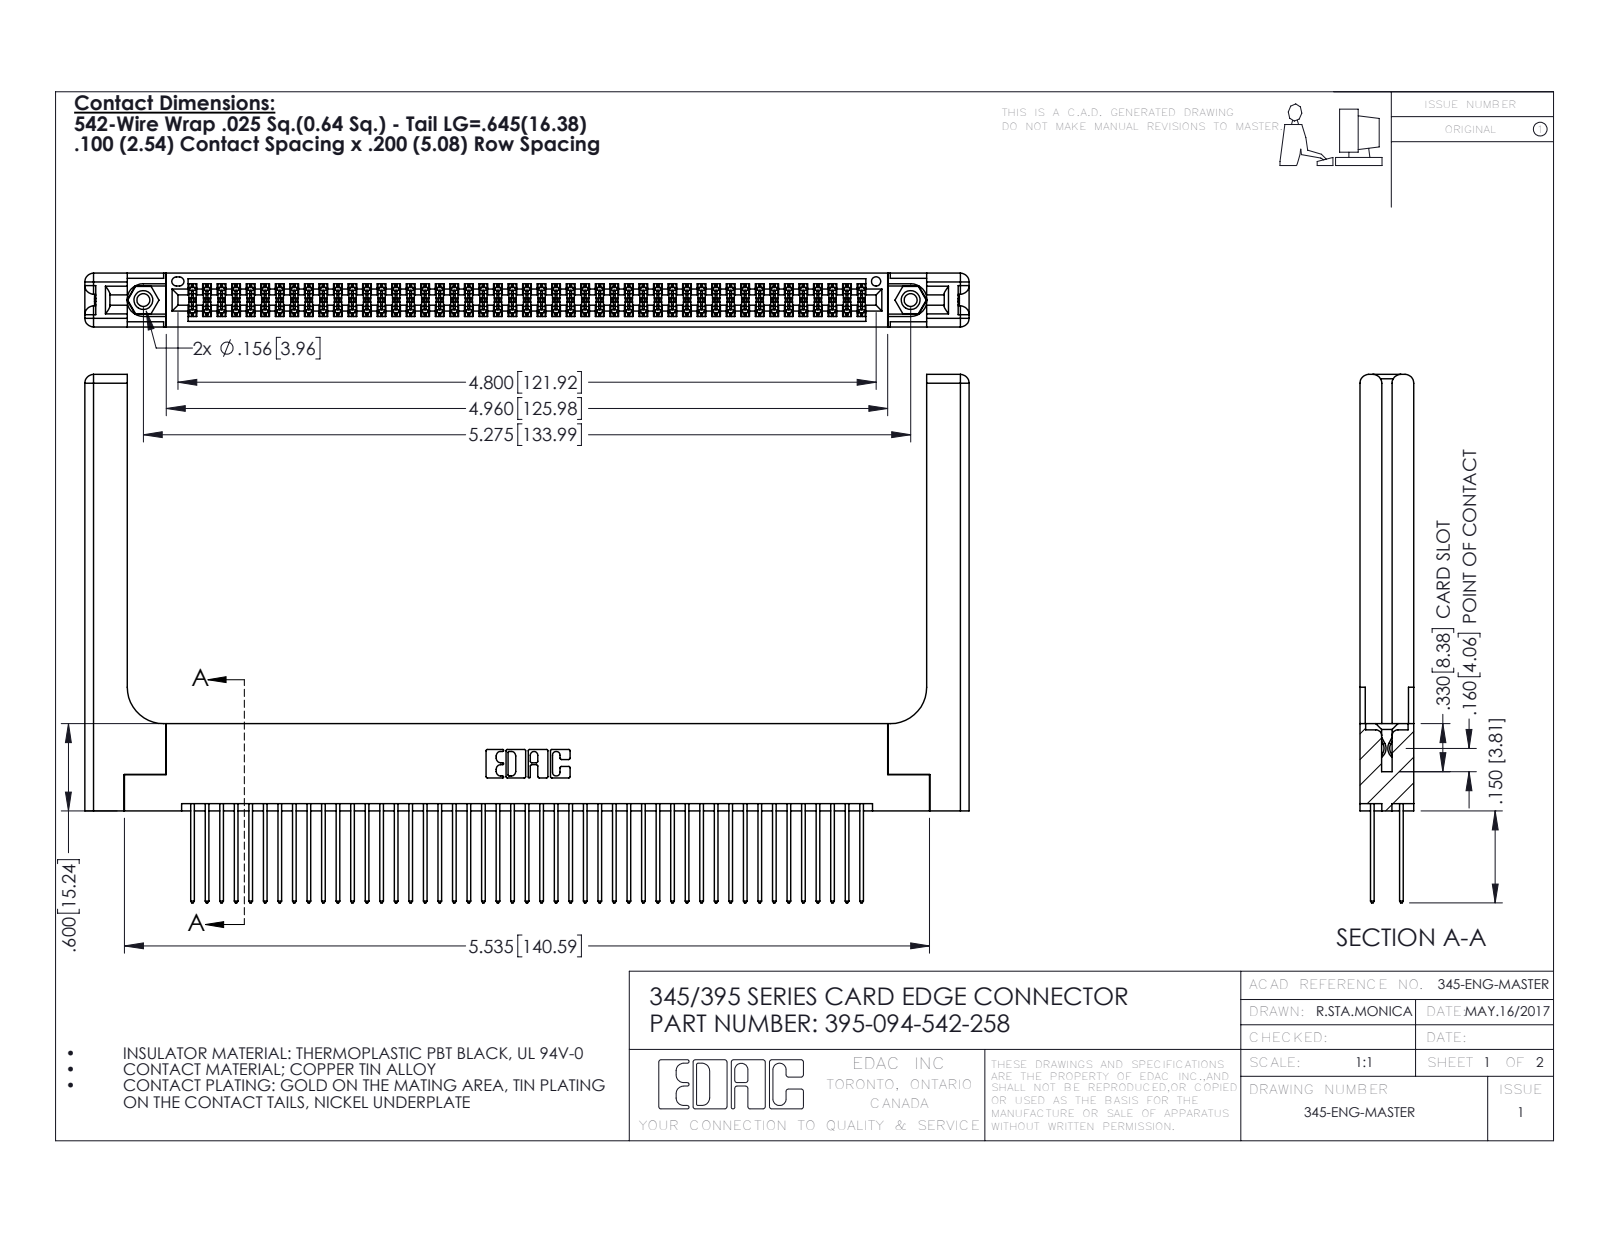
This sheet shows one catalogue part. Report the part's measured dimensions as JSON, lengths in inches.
{"part_name": "345-250-001_345-250-001-102; 395-094-542-258; 345-292-001_345-293-142; 345 Part_Flush Mounting Lugs - 0.156 Dia-TH (+1 more)", "step_written_by": "SolidWorks 2016 (CONFIG_CONTROL_DESIGN)", "units": "inches", "bodies": {"solids": 99, "faces": 5082, "planar": 3330, "cylindrical": 1692, "other": 60}, "overall_size": [6.079, 3.632, 0.37], "volume_in3": 1.462, "surface_area_in2": 46.64, "round_holes": [[0.089, 2], [0.125, 2], [0.156, 2], [0.064, 1]], "round_bosses_or_shafts": [[0.155, 2]], "partial_cylinders_radius": [[0.006, 141], [0.01, 94], [0.01, 22], [0.06, 16], [0.007, 6], [0.031, 6], [0.026, 3], [0.014, 2]], "face_to_face_distances": [0.072, 0.298, 0.37, 0.2, 0.098, 0.272, 0.025, 0.225, 0.175, 0.148], "hole_center_spacings": [0.27, 5.039, 5.275]}
